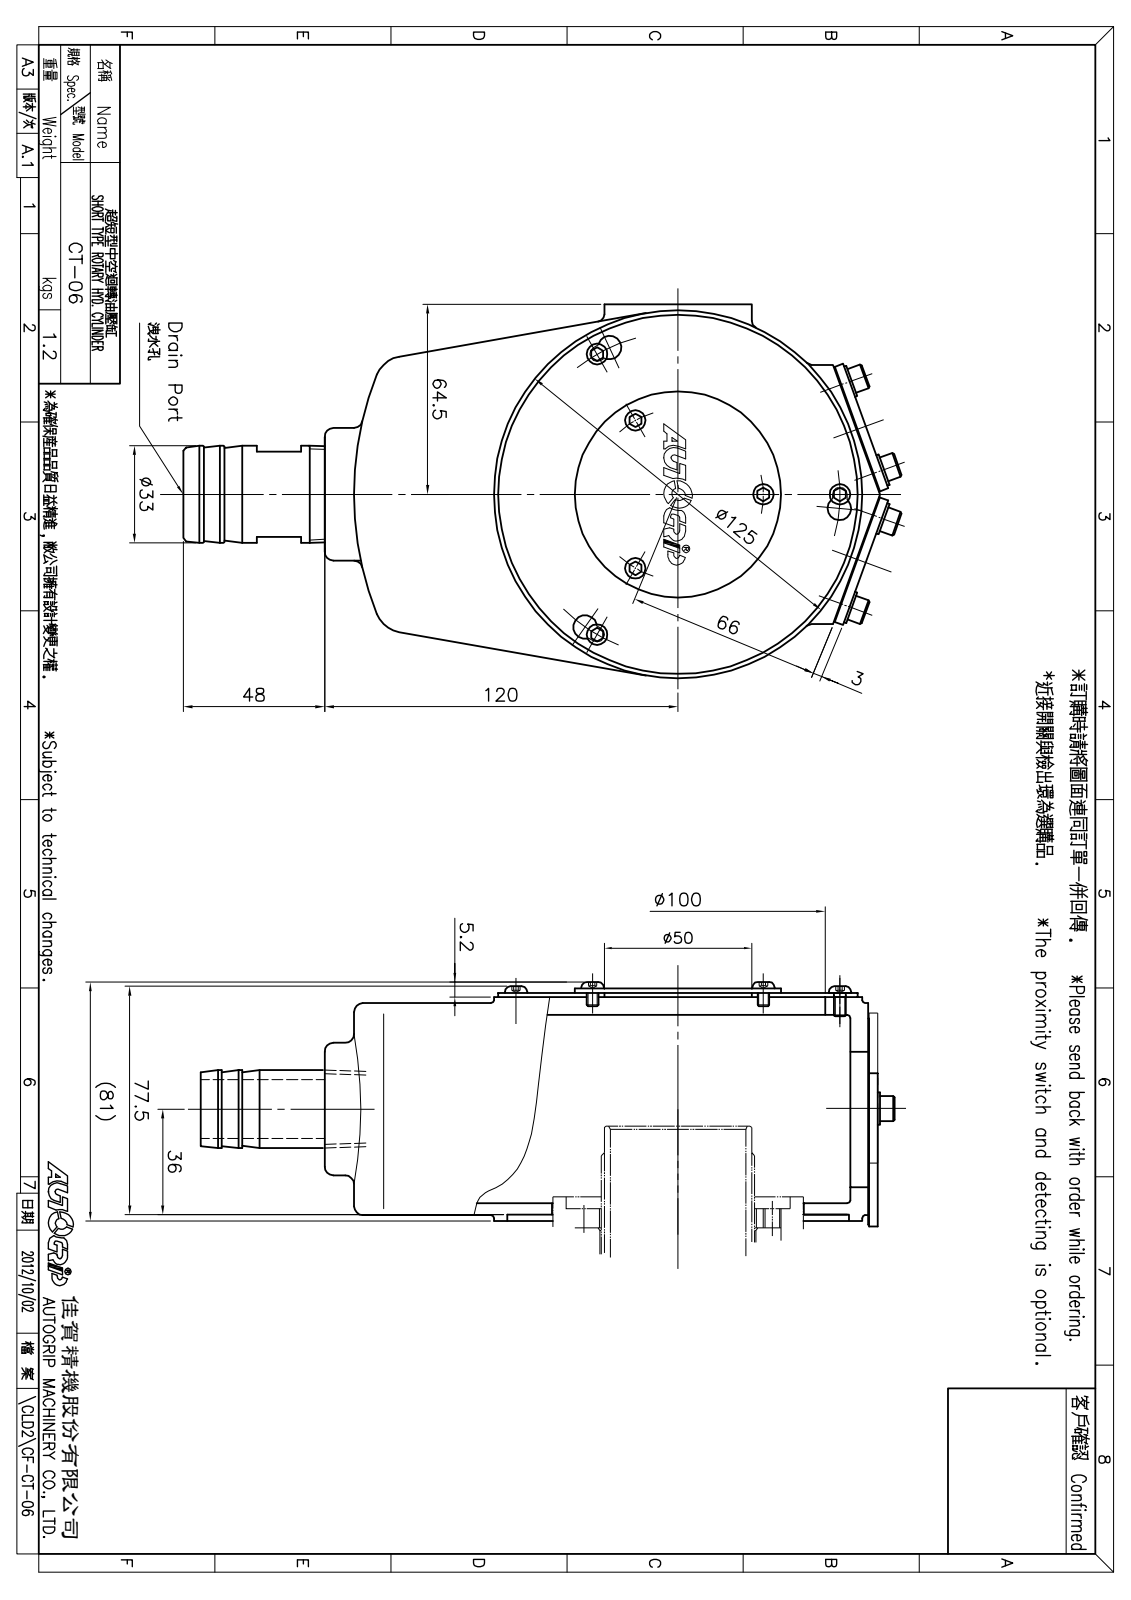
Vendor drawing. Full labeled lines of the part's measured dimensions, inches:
Part name (STEP PRODUCT): CT-08洩油管; CF-CT-06-12000; CF-CT-06-11000; CF-CT-06-09000 (+2 more)
STEP written by: SolidWorks 2016 (CONFIG_CONTROL_DESIGN)
Units: inches
Bodies: 22 solids, 551 faces (265 planar, 174 cylindrical, 112 other)
Overall size (bounding box): 9.567 × 5 × 3.189
Volume: 18.84 in³ · Surface area: 268.3 in²
Round holes (diameter × count): ⌀0.13 ×6, ⌀0.165 ×4, ⌀0.217 ×4, ⌀0.177 ×3, ⌀0.472 ×2, ⌀0.984 ×1, ⌀1.969 ×1, ⌀3.366 ×1, ⌀3.937 ×1, ⌀4.567 ×1
Round bosses / shafts (diameter × count): ⌀0.276 ×6, ⌀0.157 ×6, ⌀0.433 ×4, ⌀0.335 ×4, ⌀0.197 ×4, ⌀4.921 ×1, ⌀4.803 ×1, ⌀2.756 ×1
Partial cylindrical surfaces — rounded edges, fillets, slot ends (radius × count): R0.108 ×16, R0.118 ×10, R0.276 ×8, R0.079 ×6, R0.098 ×5, R0.157 ×3, R0.236 ×2, R0.394 ×2
Main face-to-face distances: 0.059, 0.157, 0.079, 2.756, 2.677, 2.815, 0.236, 2.913, 0.295, 2.52
Hole centre spacings: 2.909, 1.024, 1.142, 2.165, 3.75, 0.824, 0.824, 1.26
